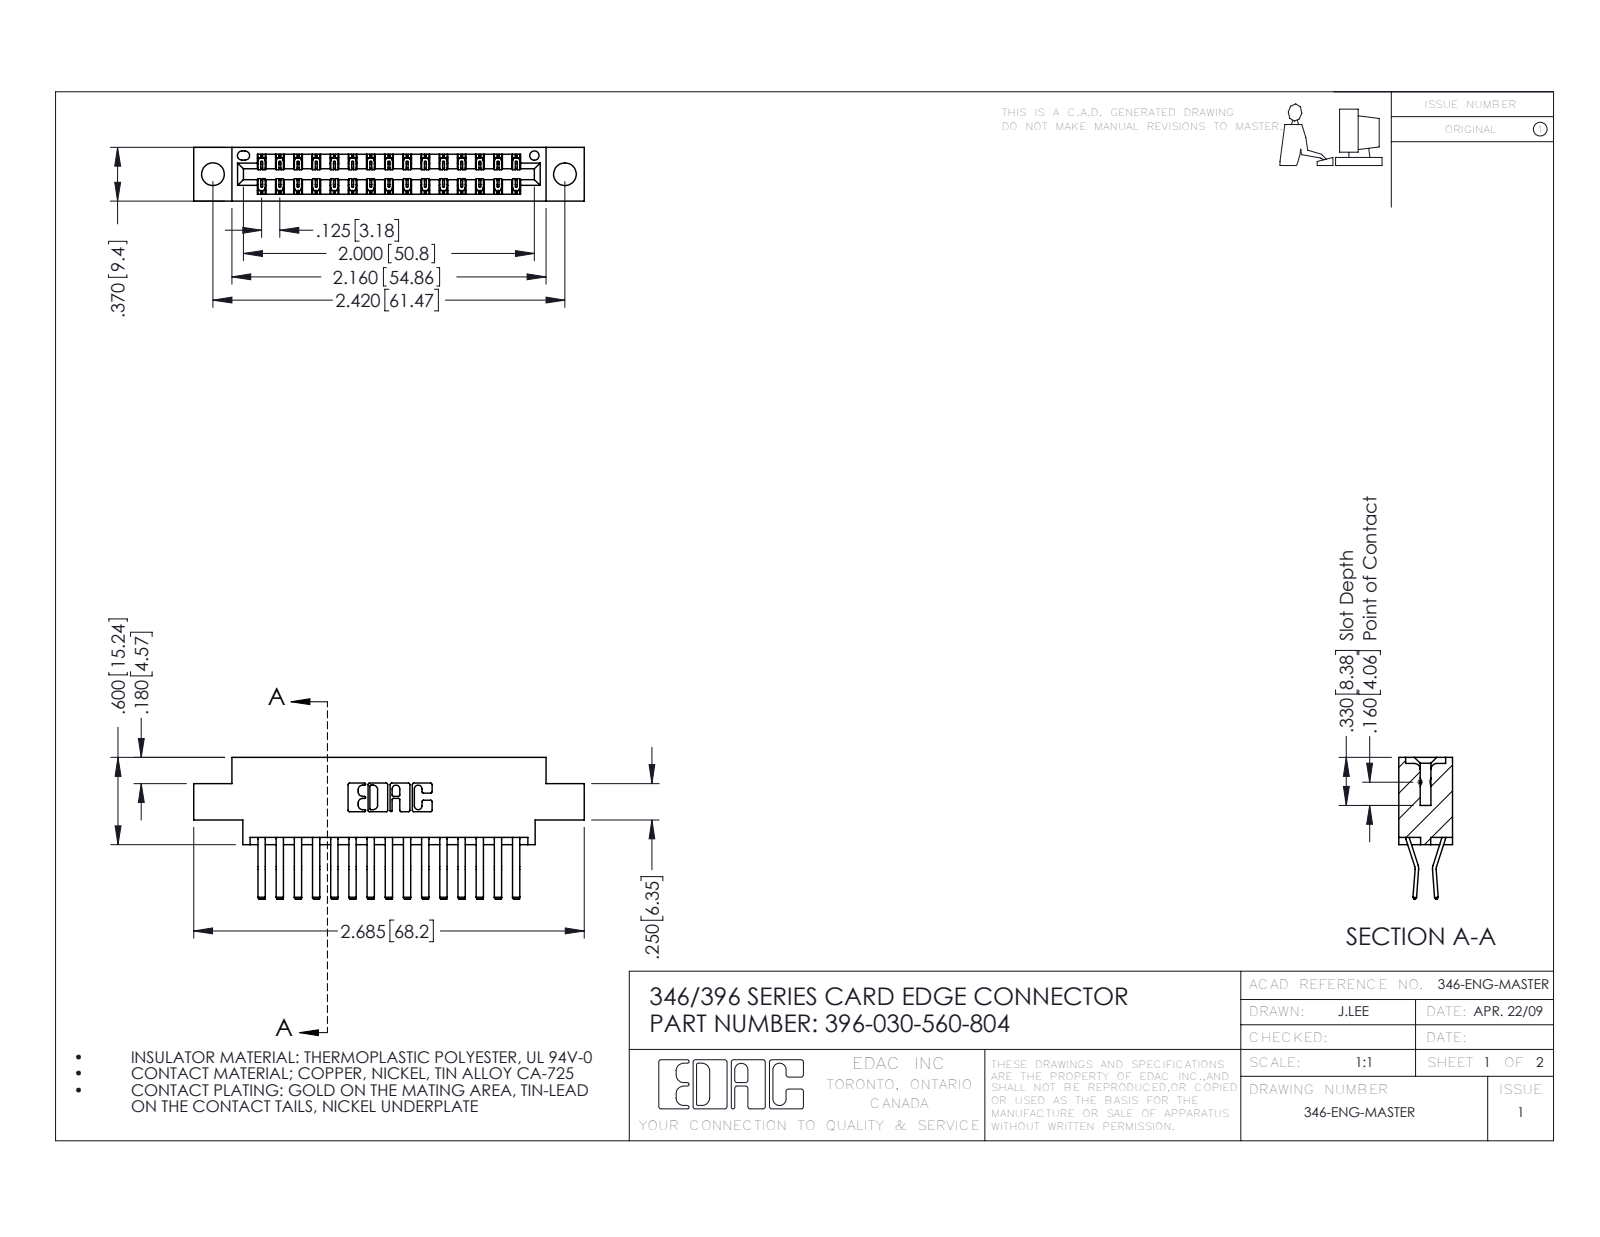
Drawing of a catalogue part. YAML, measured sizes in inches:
part_name: "345-292-001_560 Tail; 346 Part_0.170 Offset - 0.156 Dia-TH; 396-030-560-804"
step_written_by: "SolidWorks 2016 (CONFIG_CONTROL_DESIGN)"
units: inches
bodies: {solids: 31, faces: 1746, planar: 1130, cylindrical: 616, other: 0}
overall_size: [2.685, 0.975, 0.37]
volume: 0.39
surface_area: 13.77
round_holes:
  - {diameter: 0.156, count: 2}
  - {diameter: 0.064, count: 1}
partial_cylinders:
  - {radius: 0.006, count: 45}
  - {radius: 0.01, count: 22}
  - {radius: 0.007, count: 6}
  - {radius: 0.031, count: 6}
  - {radius: 0.026, count: 3}
  - {radius: 0.01, count: 2}
  - {radius: 0.014, count: 2}
  - {radius: 0.022, count: 2}
face_to_face_distances: [0.048, 0.322, 0.37, 0.25, 0.025, 0.072, 0.298, 0.275, 0.148, 0.222]
hole_center_spacings: [0.246, 2.213, 2.42]
